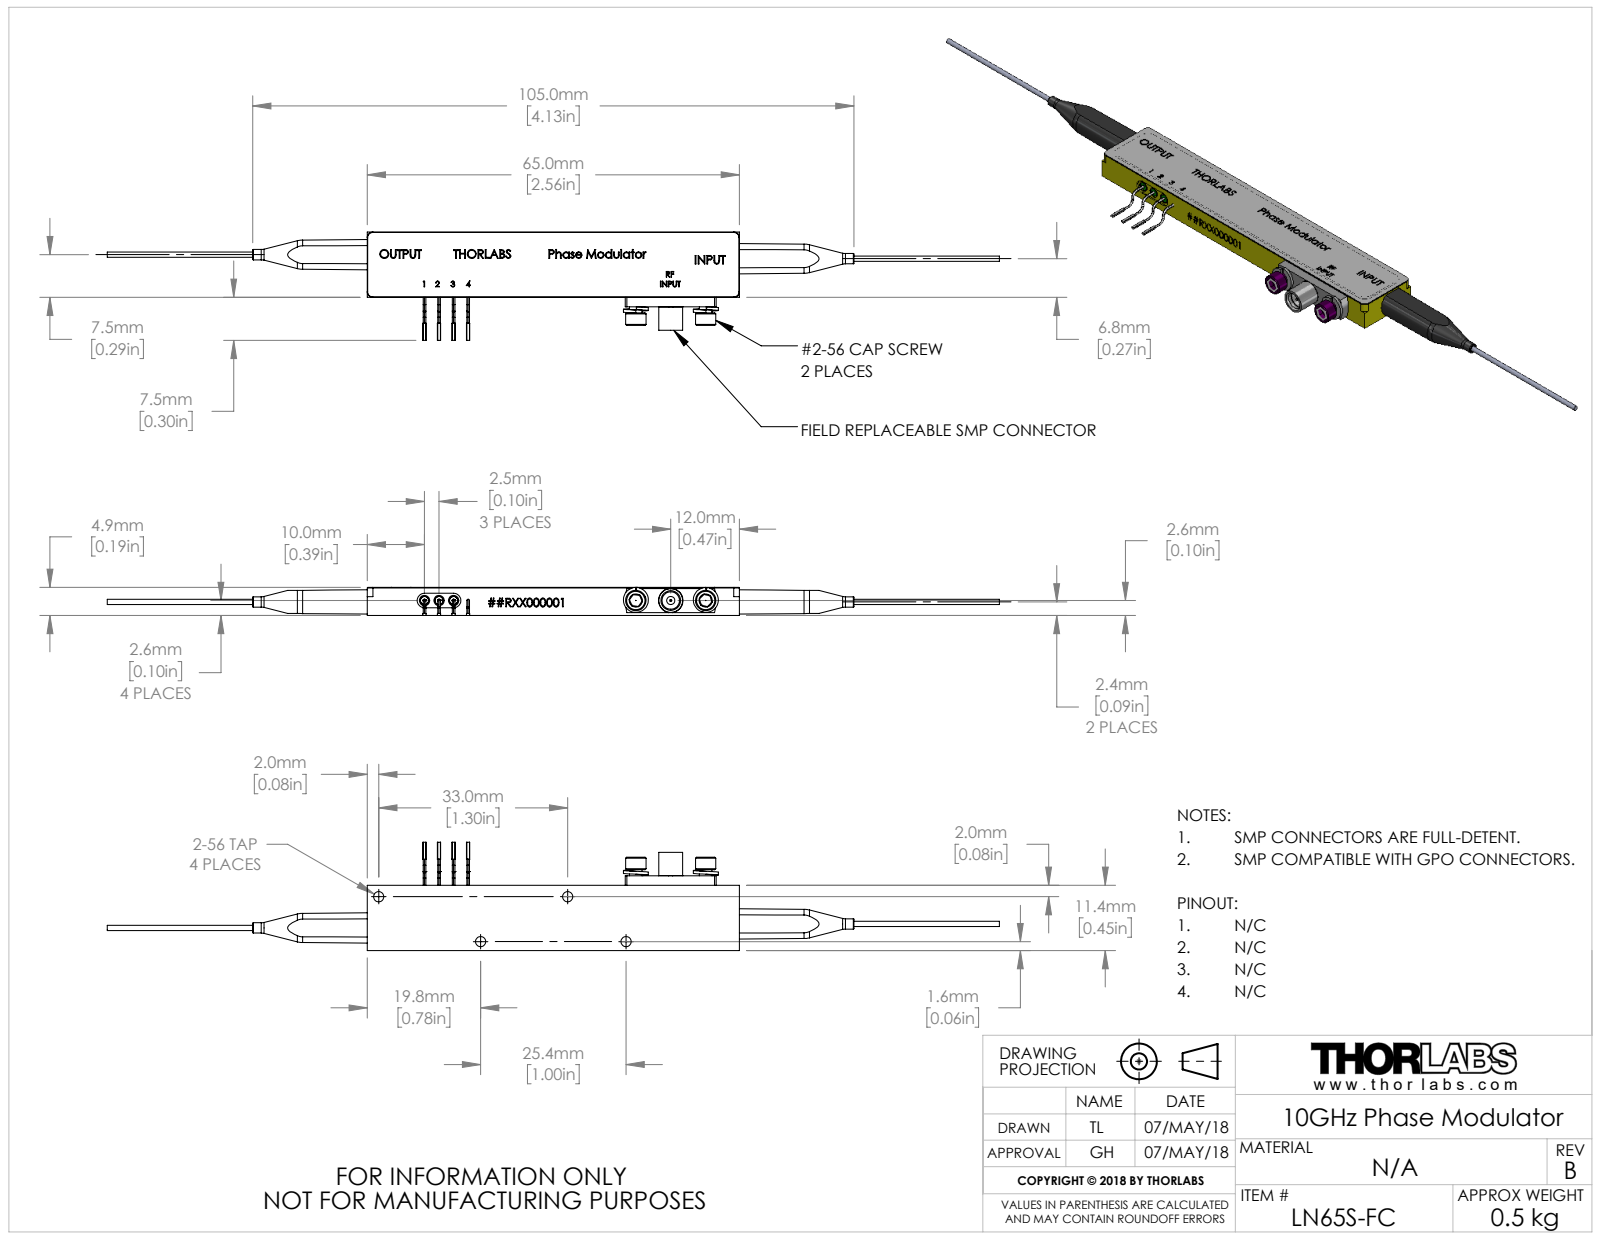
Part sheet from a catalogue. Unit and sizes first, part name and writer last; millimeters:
Units: millimetres
Overall size (bounding box): 155.8 × 18.89 × 4.91
Round holes (diameter × count): ⌀1.78 ×4, ⌀1.8 ×3, ⌀2.61 ×1, ⌀3.05 ×1, ⌀3.18 ×1
Round bosses / shafts (diameter × count): ⌀0.46 ×4, ⌀3.56 ×2, ⌀2.18 ×2, ⌀1.8 ×2, ⌀0.9 ×2, ⌀4.16 ×1, ⌀1.45 ×1, ⌀0.38 ×1
Partial cylindrical surfaces — rounded edges, fillets, slot ends (radius × count): R0.23 ×12, R0.9 ×4, R1 ×4, R1.27 ×2, R7.93 ×1
Main face-to-face distances: 4.91, 11.4, 4.78, 4.83, 65, 1.65, 13.05, 0.5, 4.7, 4.2
Hole centre spacings: 2.54, 5.08, 6.1, 12.86, 17.1, 19.45, 25.4, 33
Bodies: 0 solids, 536 faces (259 planar, 115 cylindrical, 162 other)
Part name (STEP PRODUCT): 20866-E0W
STEP written by: SolidWorks 2016 (CONFIG_CONTROL_DESIGN)
